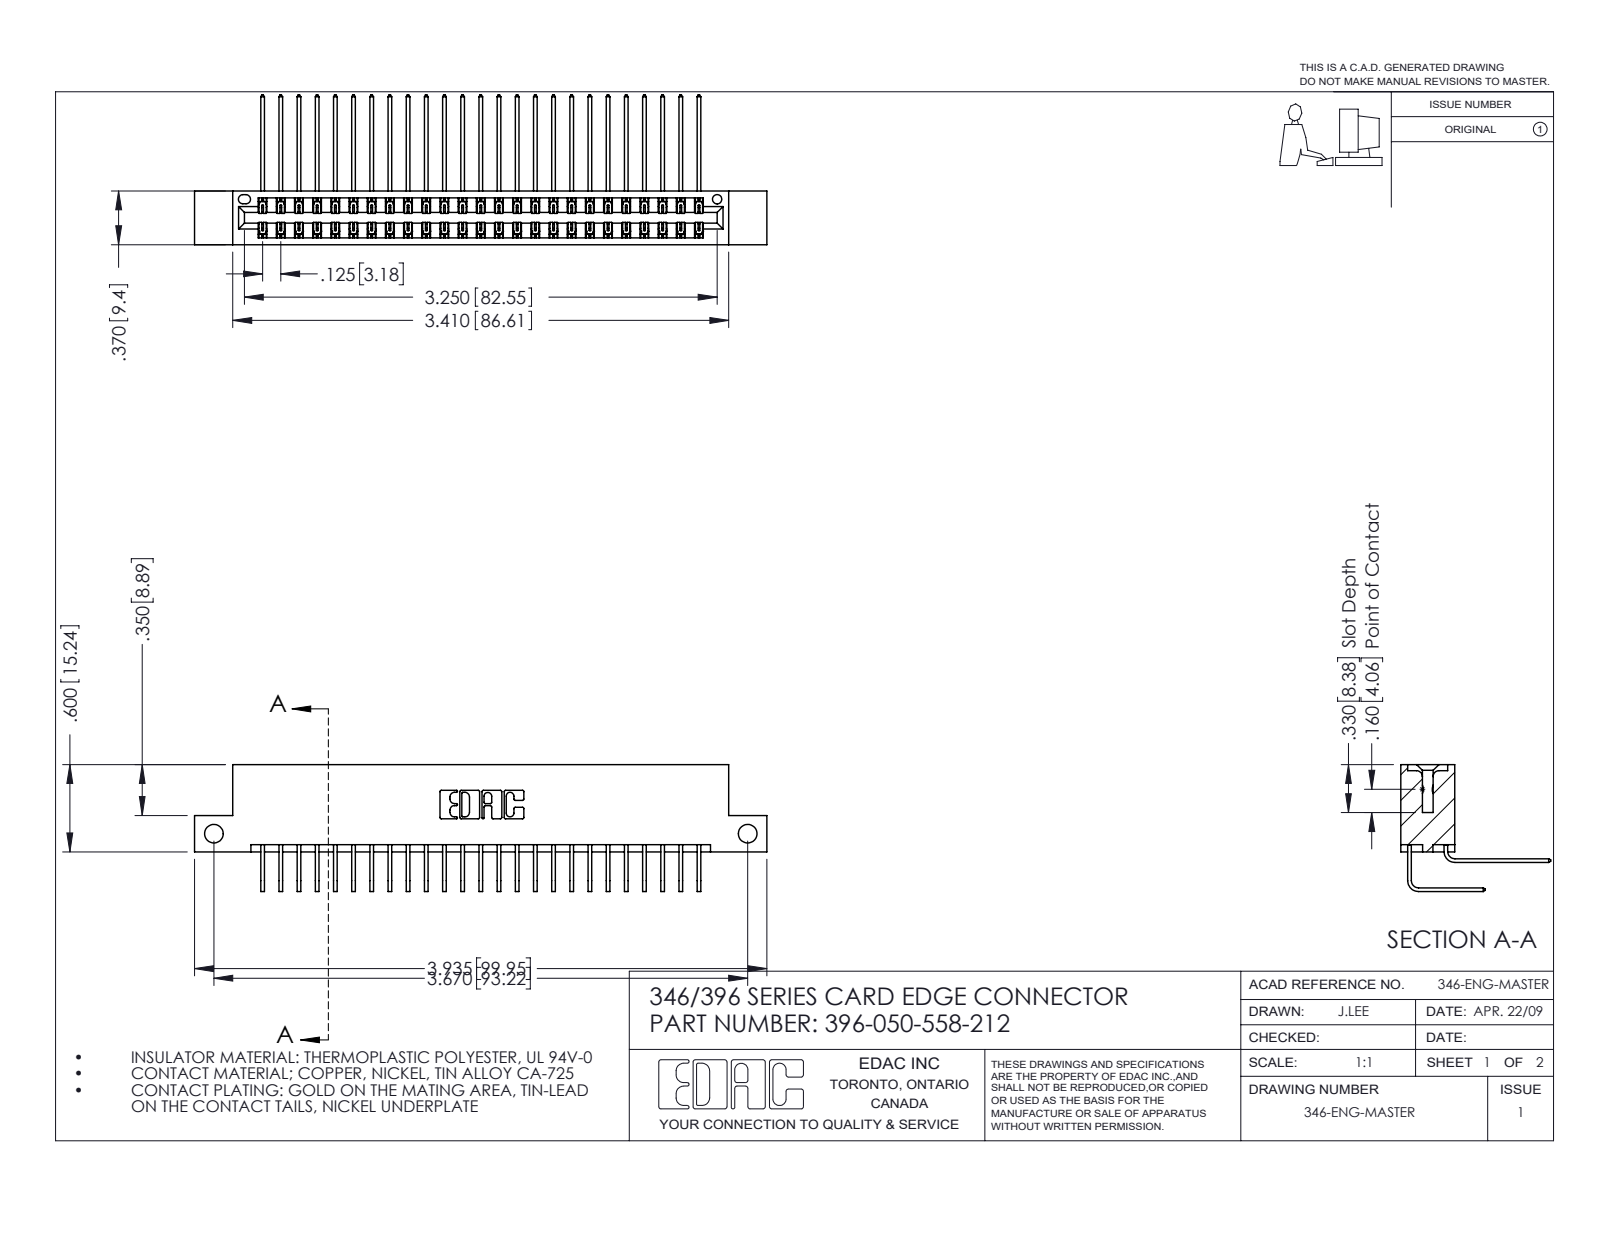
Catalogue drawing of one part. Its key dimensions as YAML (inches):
part_name: "345-292-001_558 Tail - 2; 345-292-001_558 559 Tail - 1; 346 Part_Flush Mounting Lugs - Side Mount; 396-050-558-212"
step_written_by: "SolidWorks 2016 (CONFIG_CONTROL_DESIGN)"
units: inches
bodies: {solids: 51, faces: 2822, planar: 1926, cylindrical: 896, other: 0}
overall_size: [3.935, 1.03, 0.873]
volume: 0.599
surface_area: 22.43
round_holes:
  - {diameter: 0.128, count: 2}
  - {diameter: 0.064, count: 1}
partial_cylinders:
  - {radius: 0.006, count: 75}
  - {radius: 0.01, count: 22}
  - {radius: 0.007, count: 6}
  - {radius: 0.031, count: 6}
  - {radius: 0.026, count: 3}
  - {radius: 0.014, count: 2}
  - {radius: 0.022, count: 2}
  - {radius: 0.024, count: 2}
face_to_face_distances: [0.322, 0.048, 0.025, 0.25, 0.37, 0.298, 0.072, 0.275, 0.148, 0.222]
hole_center_spacings: [3.67]
